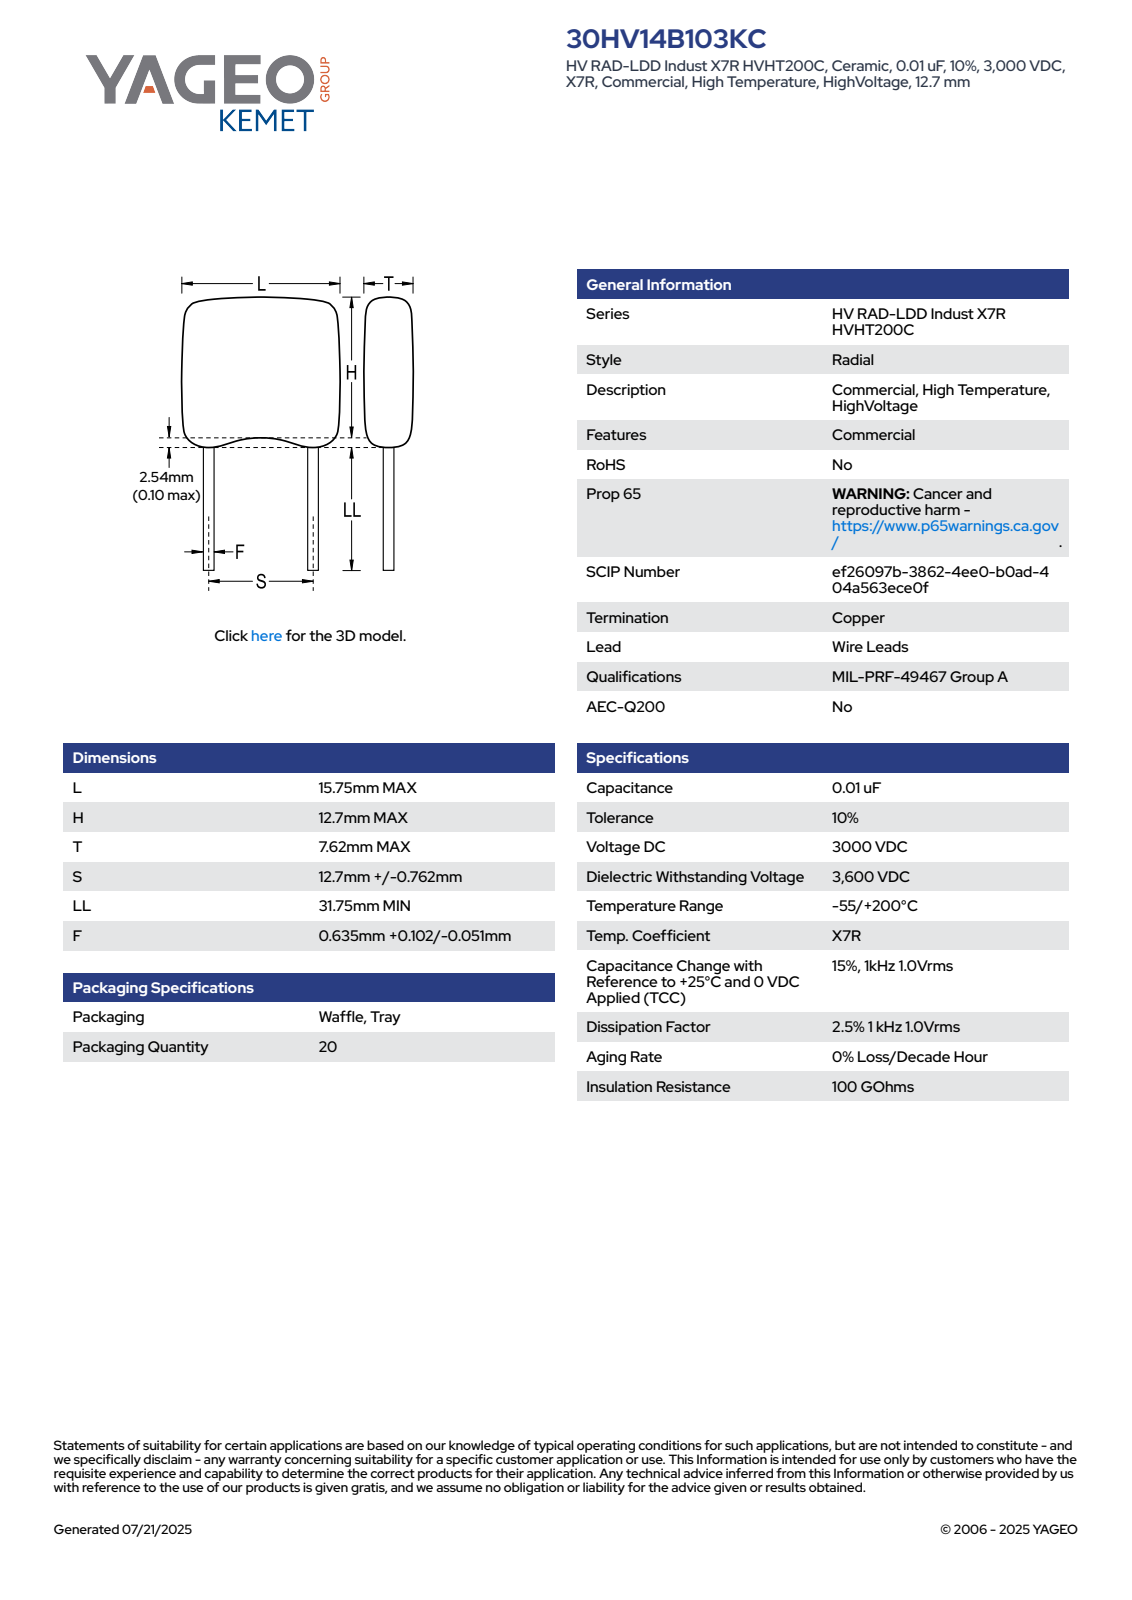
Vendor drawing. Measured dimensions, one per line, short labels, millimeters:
name: CCRM_RCST_HV14_L15.75H12.7T7.62S12.7LL3.175F0.737
written by: SolidWorks 2021 (AUTOMOTIVE_DESIGN)
unit: mm
bodies: 4 solids, 92 faces (66 planar, 16 cylindrical, 10 other)
size: 45.97 × 15.75 × 5.08
volume: 1 051 mm³; area: 832 mm²
bosses: 2× ⌀0.64
rounds: 8× R0.5, 4× R2
face distances: 5.08, 15.75, 14.22, 31.75, 45.97, 6.1, 8.12, 40.35, 8.6, 5.62
